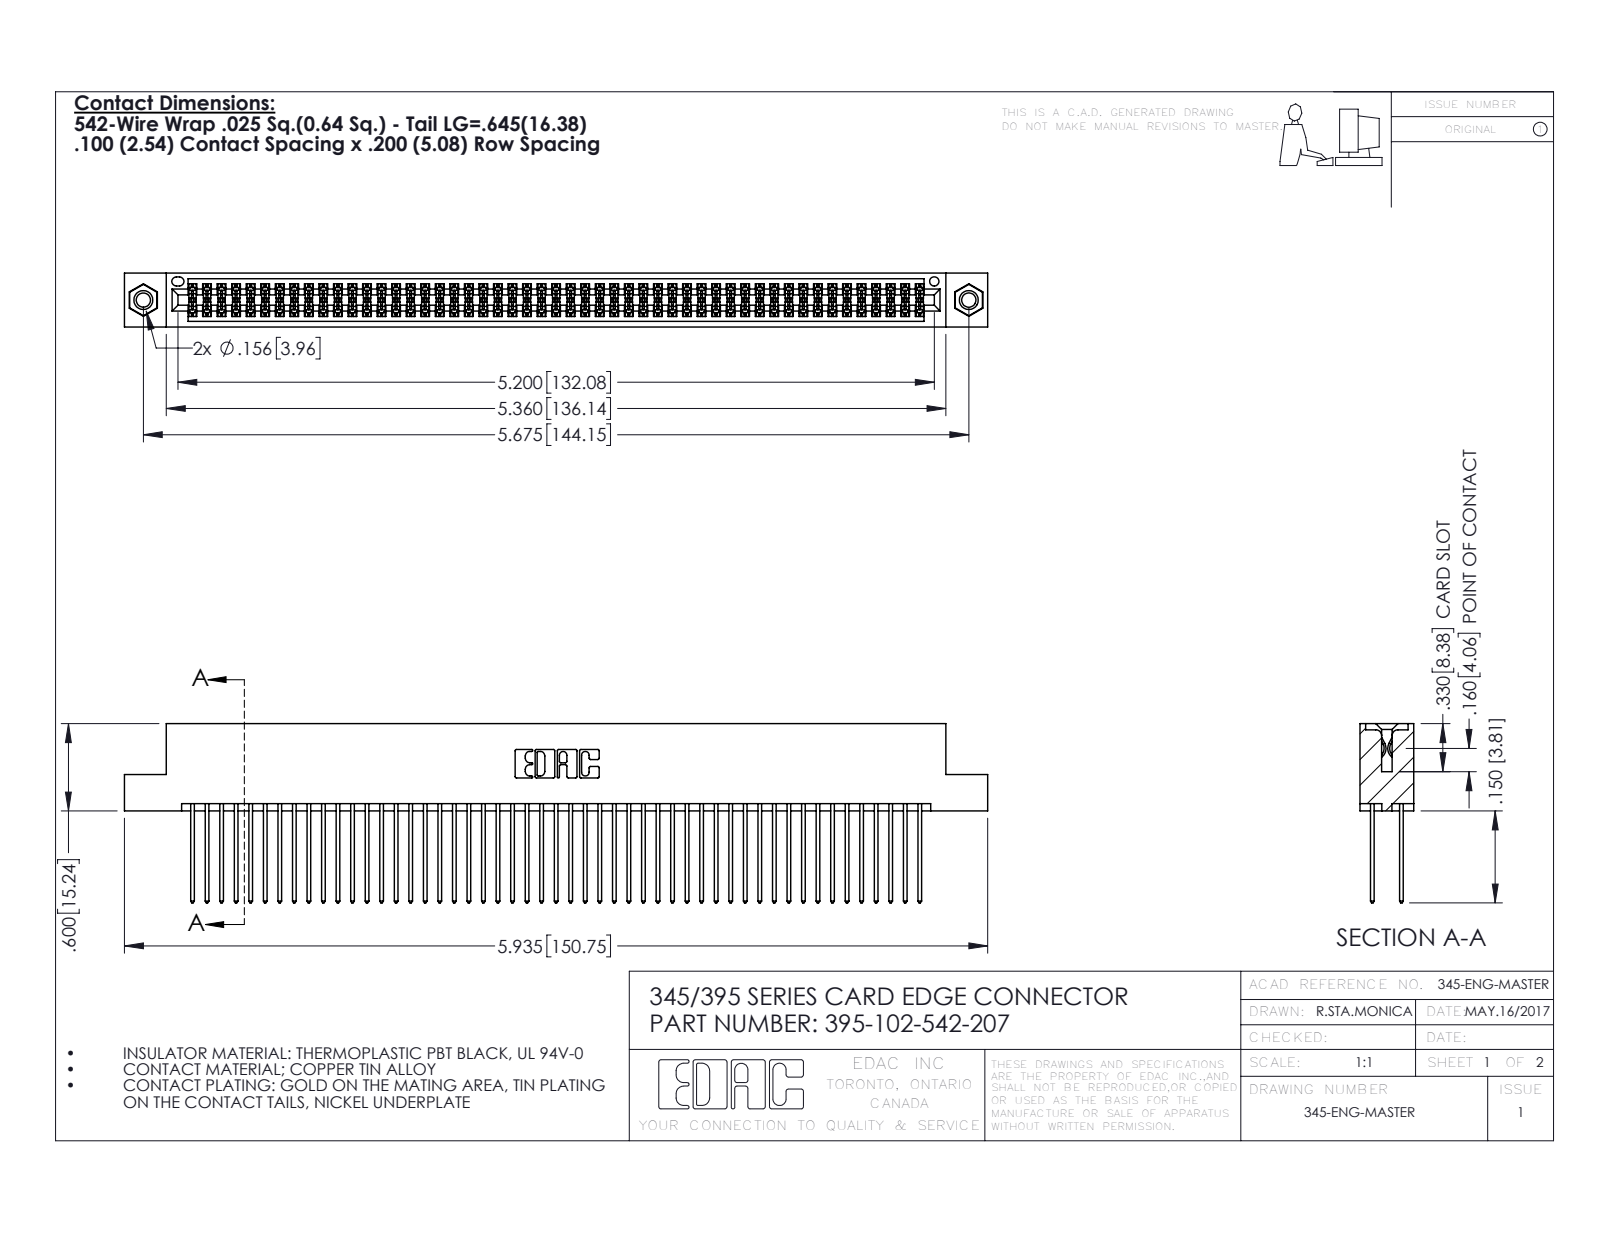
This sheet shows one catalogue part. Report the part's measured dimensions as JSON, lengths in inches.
{"part_name": "395-102-542-207; 345 Part_Flush Mounting Lugs - 0.156 Dia-TI; 345-250-001_345-250-005-103; 345-292-001_345-293-142", "step_written_by": "SolidWorks 2016 (CONFIG_CONTROL_DESIGN)", "units": "inches", "bodies": {"solids": 105, "faces": 5286, "planar": 3478, "cylindrical": 1792, "other": 16}, "overall_size": [5.935, 1.232, 0.37], "volume_in3": 0.927, "surface_area_in2": 38.56, "round_holes": [[0.098, 2], [0.125, 2], [0.156, 2], [0.064, 1]], "round_bosses_or_shafts": [[0.155, 2]], "partial_cylinders_radius": [[0.006, 153], [0.01, 102], [0.01, 22], [0.007, 6], [0.031, 6], [0.026, 3], [0.014, 2], [0.019, 2]], "face_to_face_distances": [0.072, 0.298, 0.2, 0.098, 0.272, 0.025, 0.225, 0.37, 0.175, 0.149], "hole_center_spacings": [0.27, 5.439, 5.675]}
